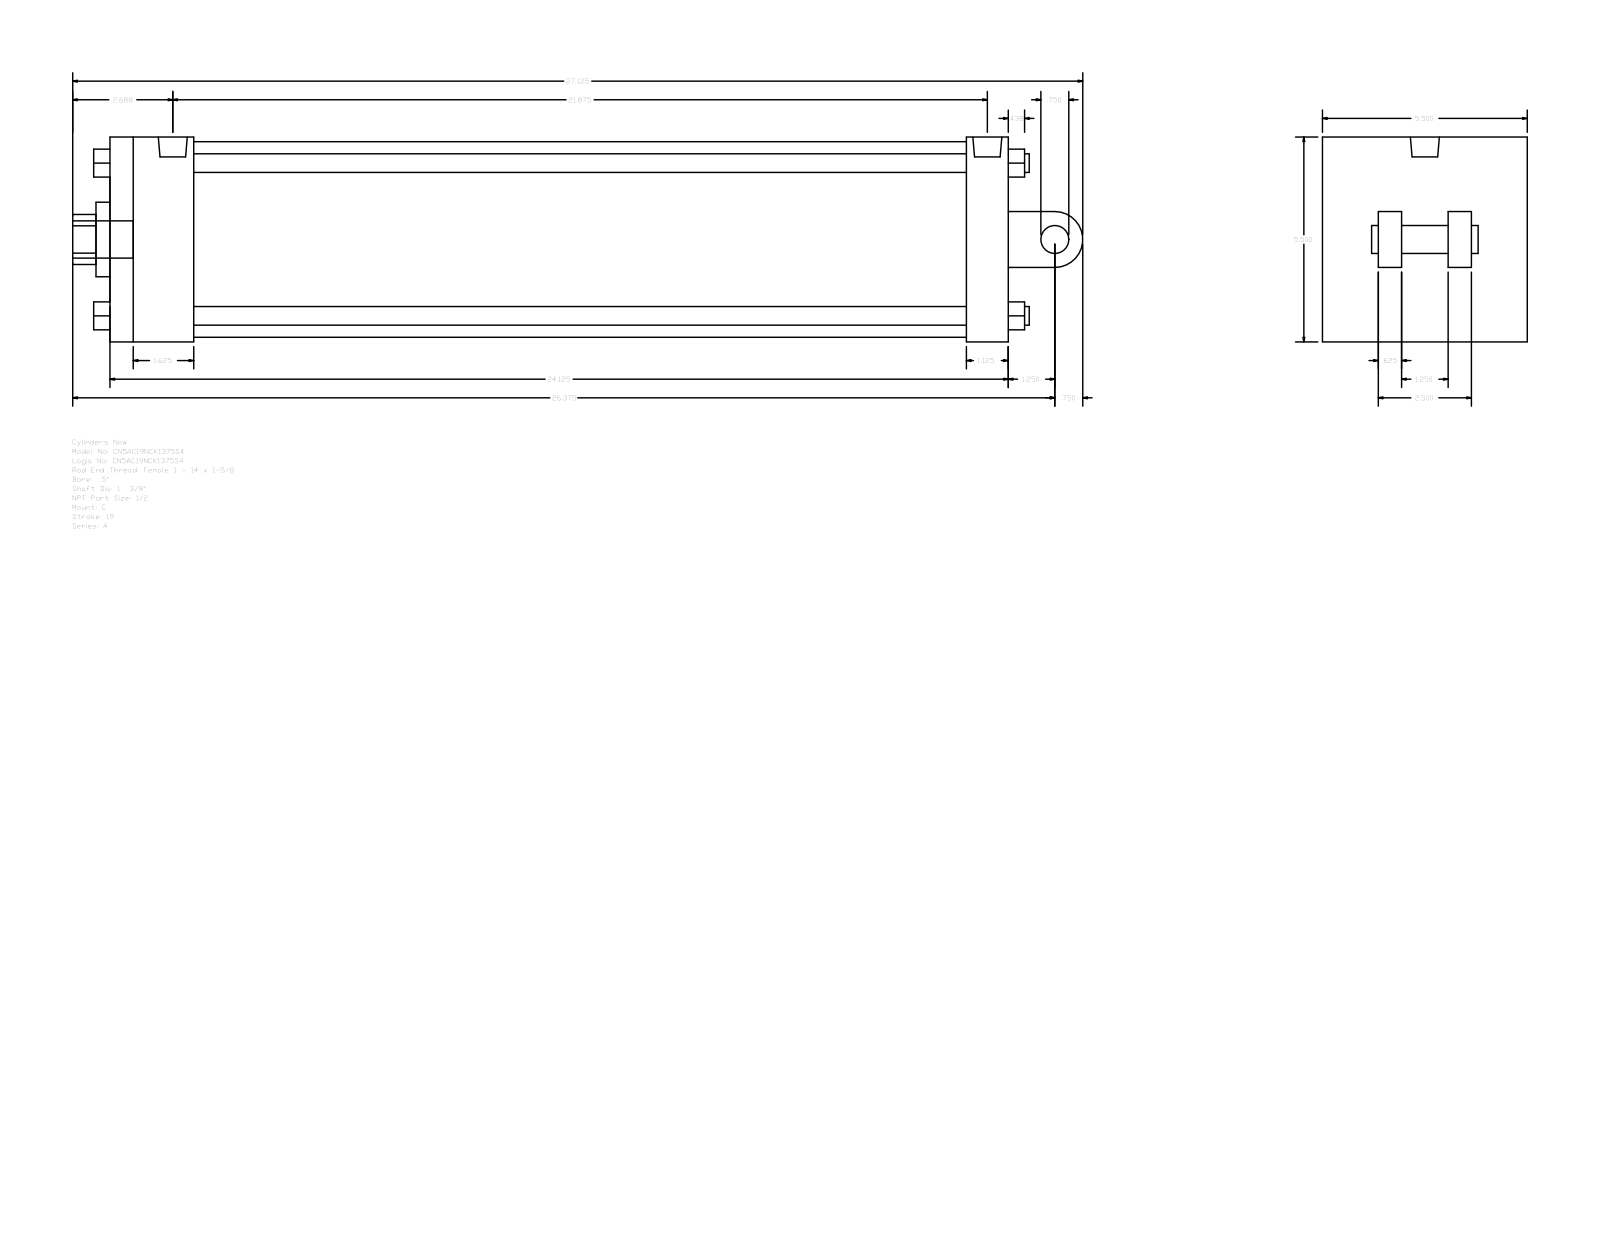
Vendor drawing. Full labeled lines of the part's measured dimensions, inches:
Part name (STEP PRODUCT): A_C__0500_1.375
STEP written by: GSSL Pune (CONFIG_CONTROL_DESIGN)
Units: inches
Bodies: 0 solids, 135 faces (102 planar, 33 cylindrical, 0 other)
Overall size (bounding box): 27.125 × 5.5 × 5.5
Round holes (diameter × count): ⌀0.344 ×2, ⌀0.778 ×1, ⌀1.375 ×1, ⌀2 ×1, ⌀5.25 ×1
Round bosses / shafts (diameter × count): ⌀0.5 ×4, ⌀0.344 ×2, ⌀1 ×1, ⌀0.778 ×1, ⌀0.75 ×1
Partial cylindrical surfaces — rounded edges, fillets, slot ends (radius × count): R0.672 ×1, R0.75 ×1
Main face-to-face distances: 5.5, 24.125, 1.125, 2.25, 23, 20.75, 21.875, 1.5, 0.625, 2.125
Hole centre spacings: 0.094
